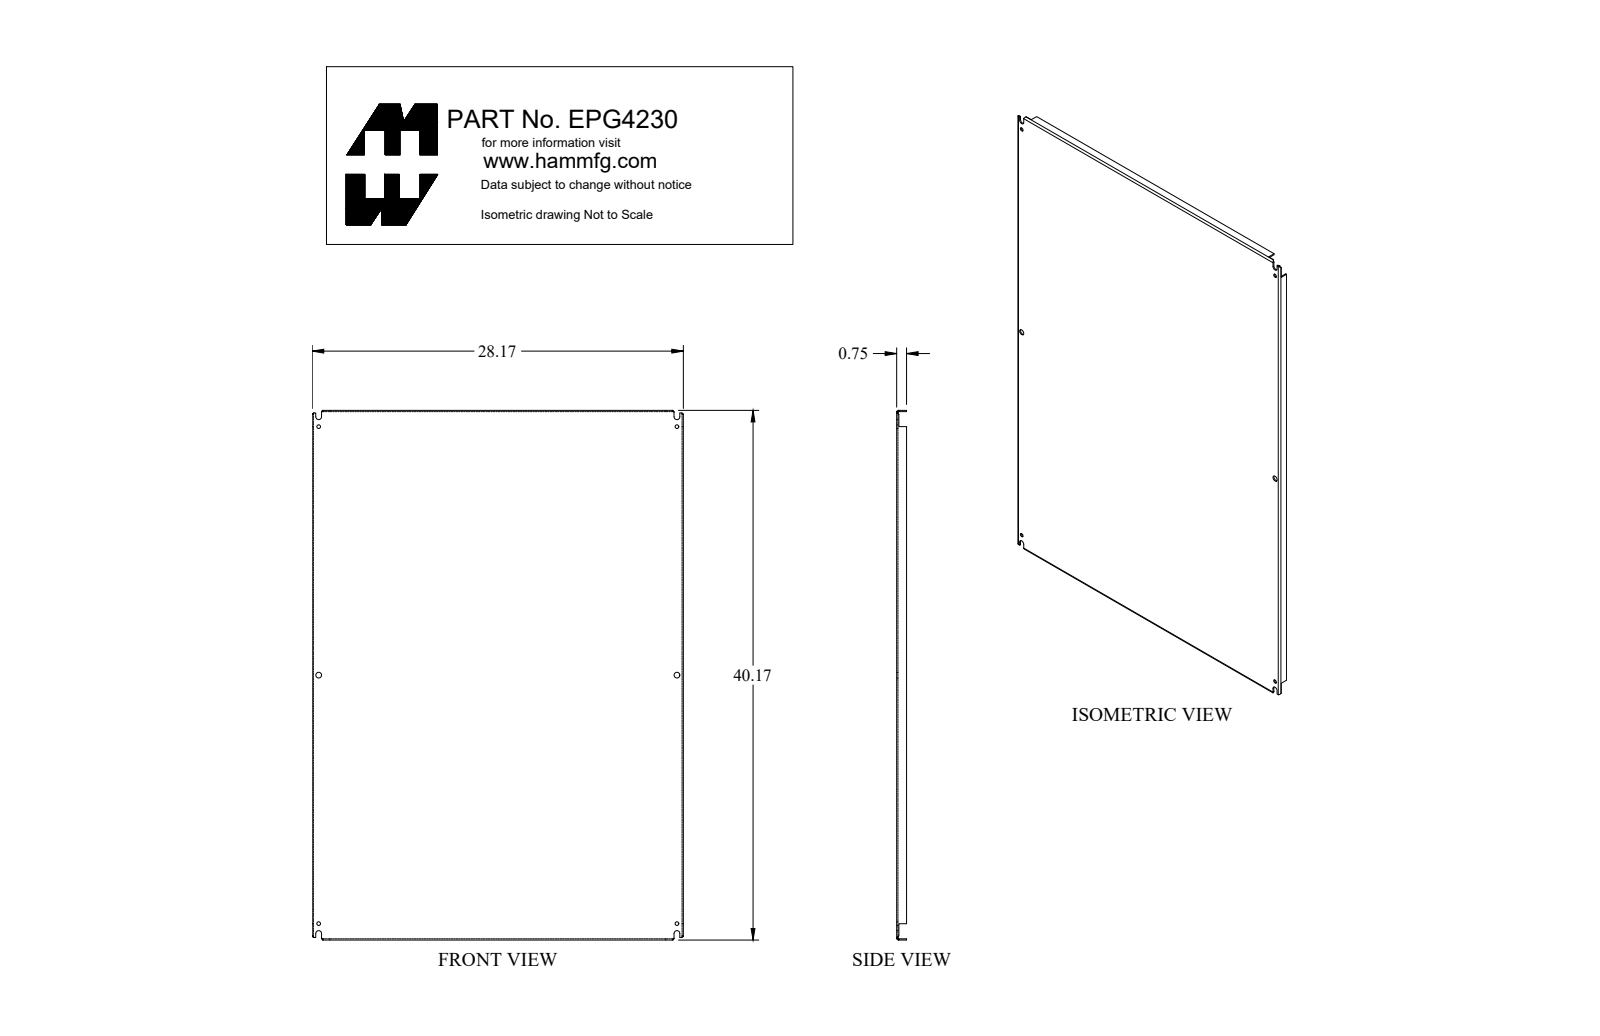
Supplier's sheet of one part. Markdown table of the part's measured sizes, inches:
| quantity | value |
| --- | --- |
| part name | EPG4230 |
| STEP written by | SolidWorks 2018 (AUTOMOTIVE_DESIGN) |
| units | inches |
| bodies | 1 solid, 132 faces (74 planar, 42 cylindrical, 16 other) |
| overall size | 40.17 × 28.17 × 0.75 |
| volume | 114.7 in³ |
| surface area | 2 429 in² |
| round holes (diameter × count) | 0.281 × 4, 0.437 × 2 |
| partial cylindrical surfaces (radius × count) | 0.048 × 4, 0.063 × 4, 0.143 × 4, 0.219 × 4 |
| main face-to-face distances | 0.095, 28.075, 40.075, 27.98, 28.17, 39.98, 40.17, 0.75, 0.655, 0.171 |
| hole center spacings | 18.844, 33.08, 27.188, 37.688, 46.472 |
